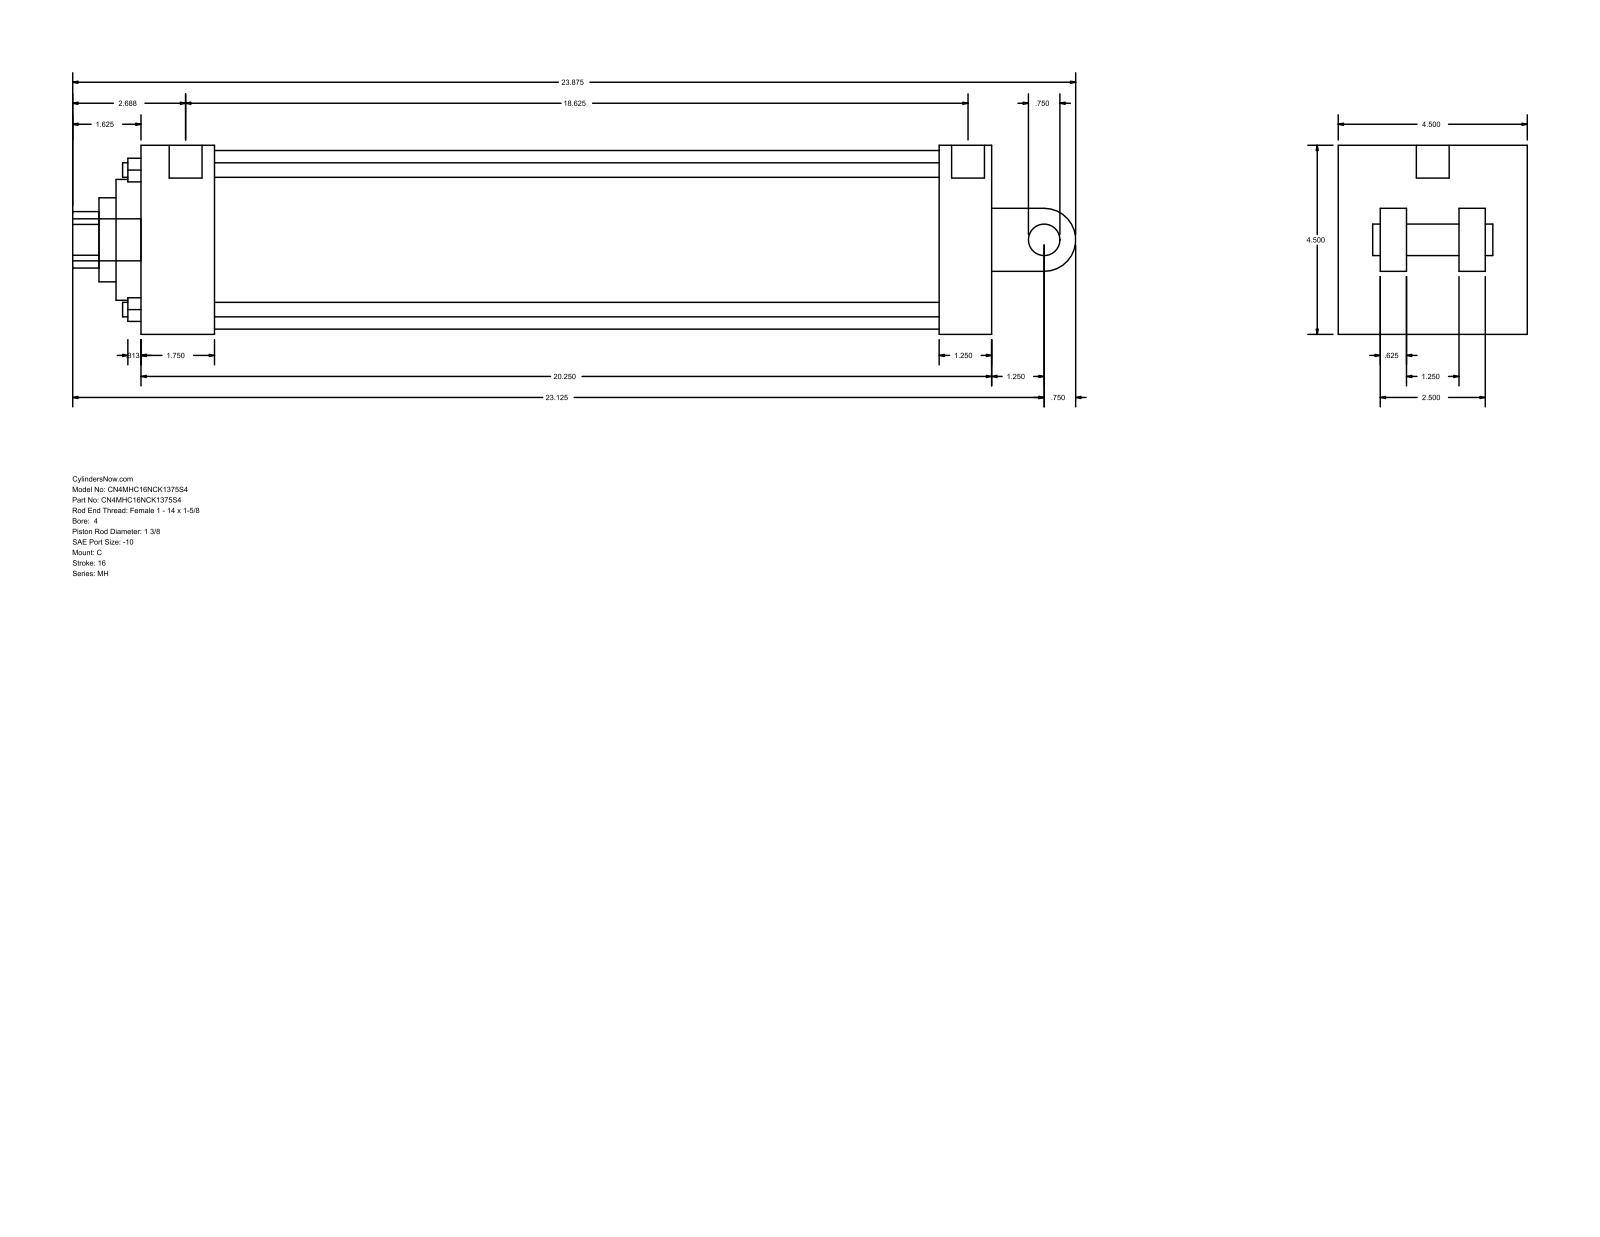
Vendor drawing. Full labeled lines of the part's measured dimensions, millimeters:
Part name (STEP PRODUCT): MH_C__0400_1.375
STEP written by: GSSL Pune (CONFIG_CONTROL_DESIGN)
Units: millimetres
Bodies: 0 solids, 101 faces (71 planar, 30 cylindrical, 0 other)
Overall size (bounding box): 606.42 × 114.3 × 114.3
Round holes (diameter × count): ⌀8.76 ×4, ⌀8.73 ×2, ⌀19.84 ×1, ⌀34.92 ×1, ⌀50.8 ×1, ⌀73.03 ×1, ⌀107.95 ×1
Round bosses / shafts (diameter × count): ⌀8.73 ×2, ⌀25.4 ×1, ⌀19.84 ×1, ⌀19.05 ×1
Partial cylindrical surfaces — rounded edges, fillets, slot ends (radius × count): R17.06 ×1, R19.05 ×1
Main face-to-face distances: 114.3, 514.35, 44.45, 482.61, 438.16, 469.9, 31.74, 73.03, 41.27, 38.1
Hole centre spacings: 59.62, 84.32, 119.25, 1.58
